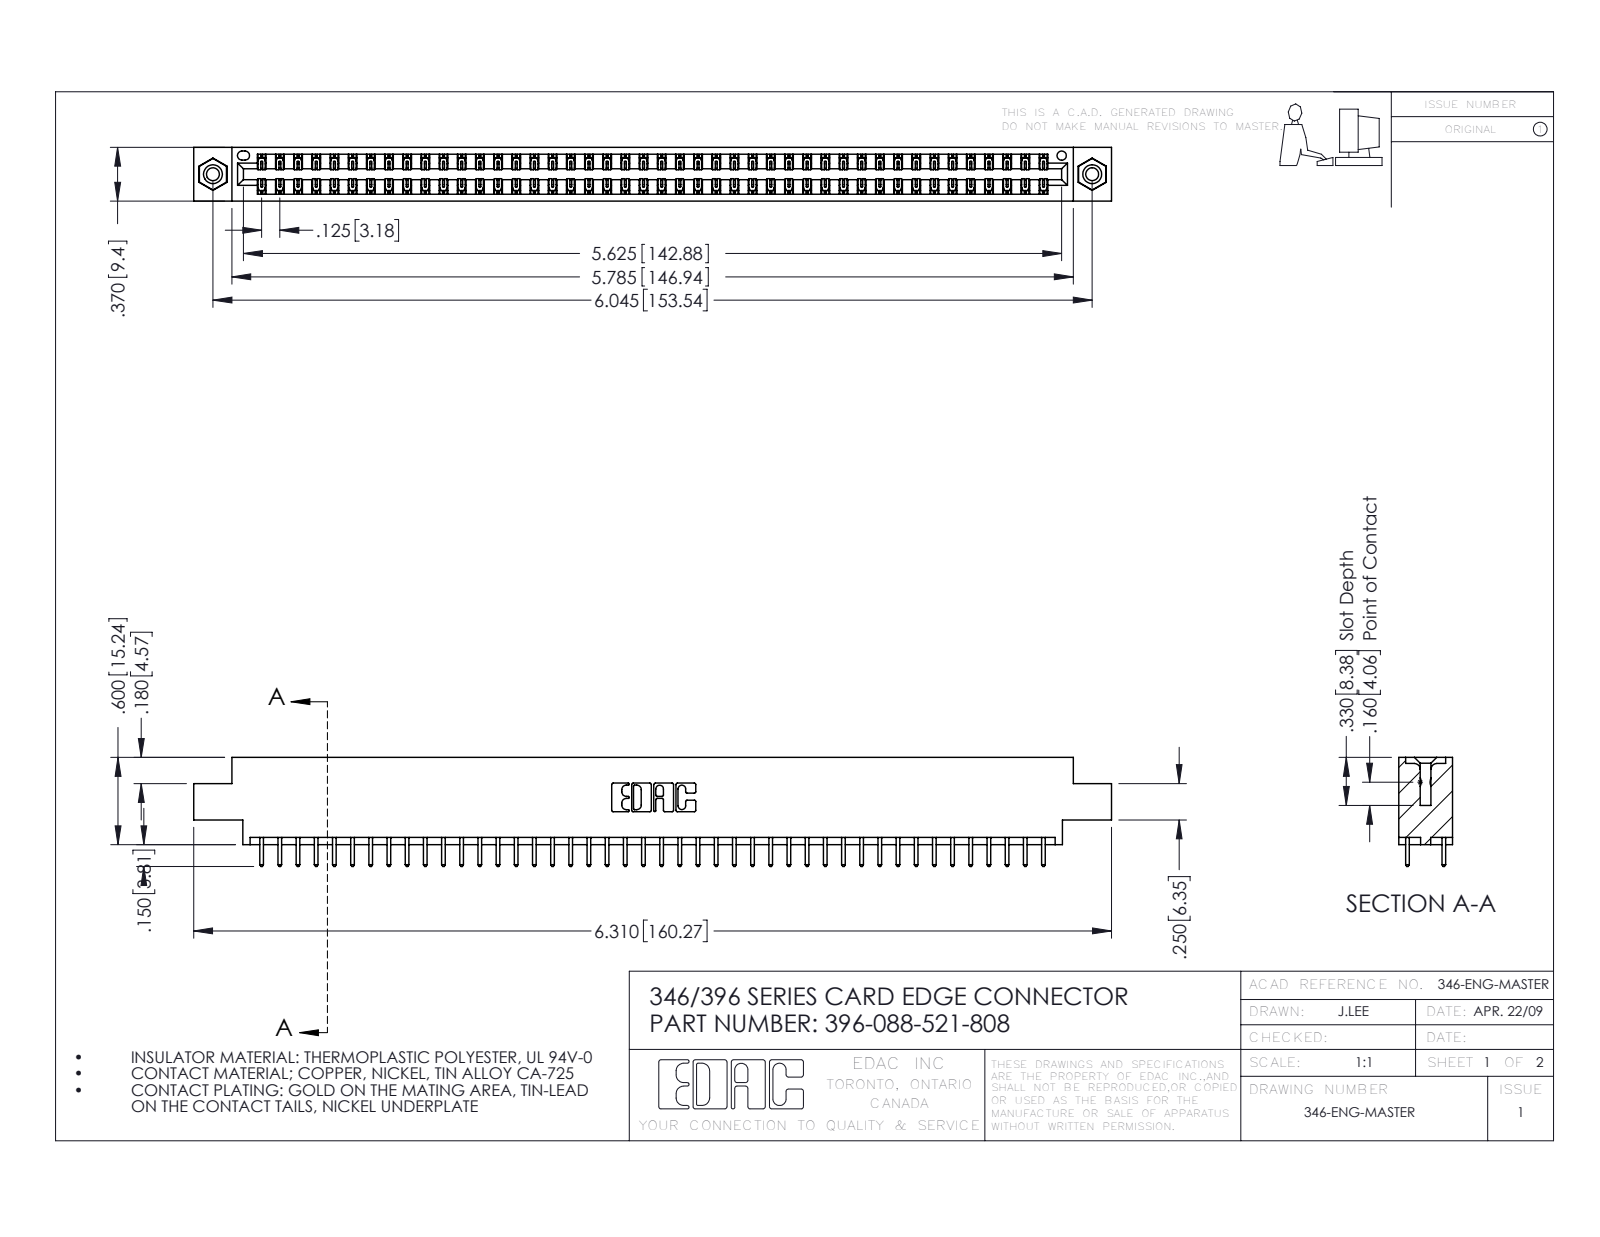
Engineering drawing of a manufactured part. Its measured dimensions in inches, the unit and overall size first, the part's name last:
Units: inches
Overall size (bounding box): 6.31 × 0.75 × 0.37
Round holes (diameter × count): ⌀0.089 ×2, ⌀0.125 ×2, ⌀0.156 ×2, ⌀0.064 ×1
Round bosses / shafts (diameter × count): ⌀0.155 ×2
Partial cylindrical surfaces — rounded edges, fillets, slot ends (radius × count): R0.006 ×132, R0.01 ×88, R0.01 ×22, R0.007 ×6, R0.031 ×6, R0.026 ×3, R0.014 ×2, R0.022 ×2
Main face-to-face distances: 0.048, 0.322, 0.37, 0.25, 0.072, 0.298, 0.025, 0.275, 0.222, 0.148
Hole centre spacings: 0.246, 5.836, 6.045
Volume: 0.943 in³ · Surface area: 32.89 in²
Bodies: 91 solids, 4762 faces (3192 planar, 1554 cylindrical, 16 other)
Part name (STEP PRODUCT): 346 Part_0.170 Offset - 0.156 Dia-TI; 345-250-001_345-250-003-102; 345-292-001_345-293-121; 396-088-521-808
STEP written by: SolidWorks 2016 (CONFIG_CONTROL_DESIGN)
